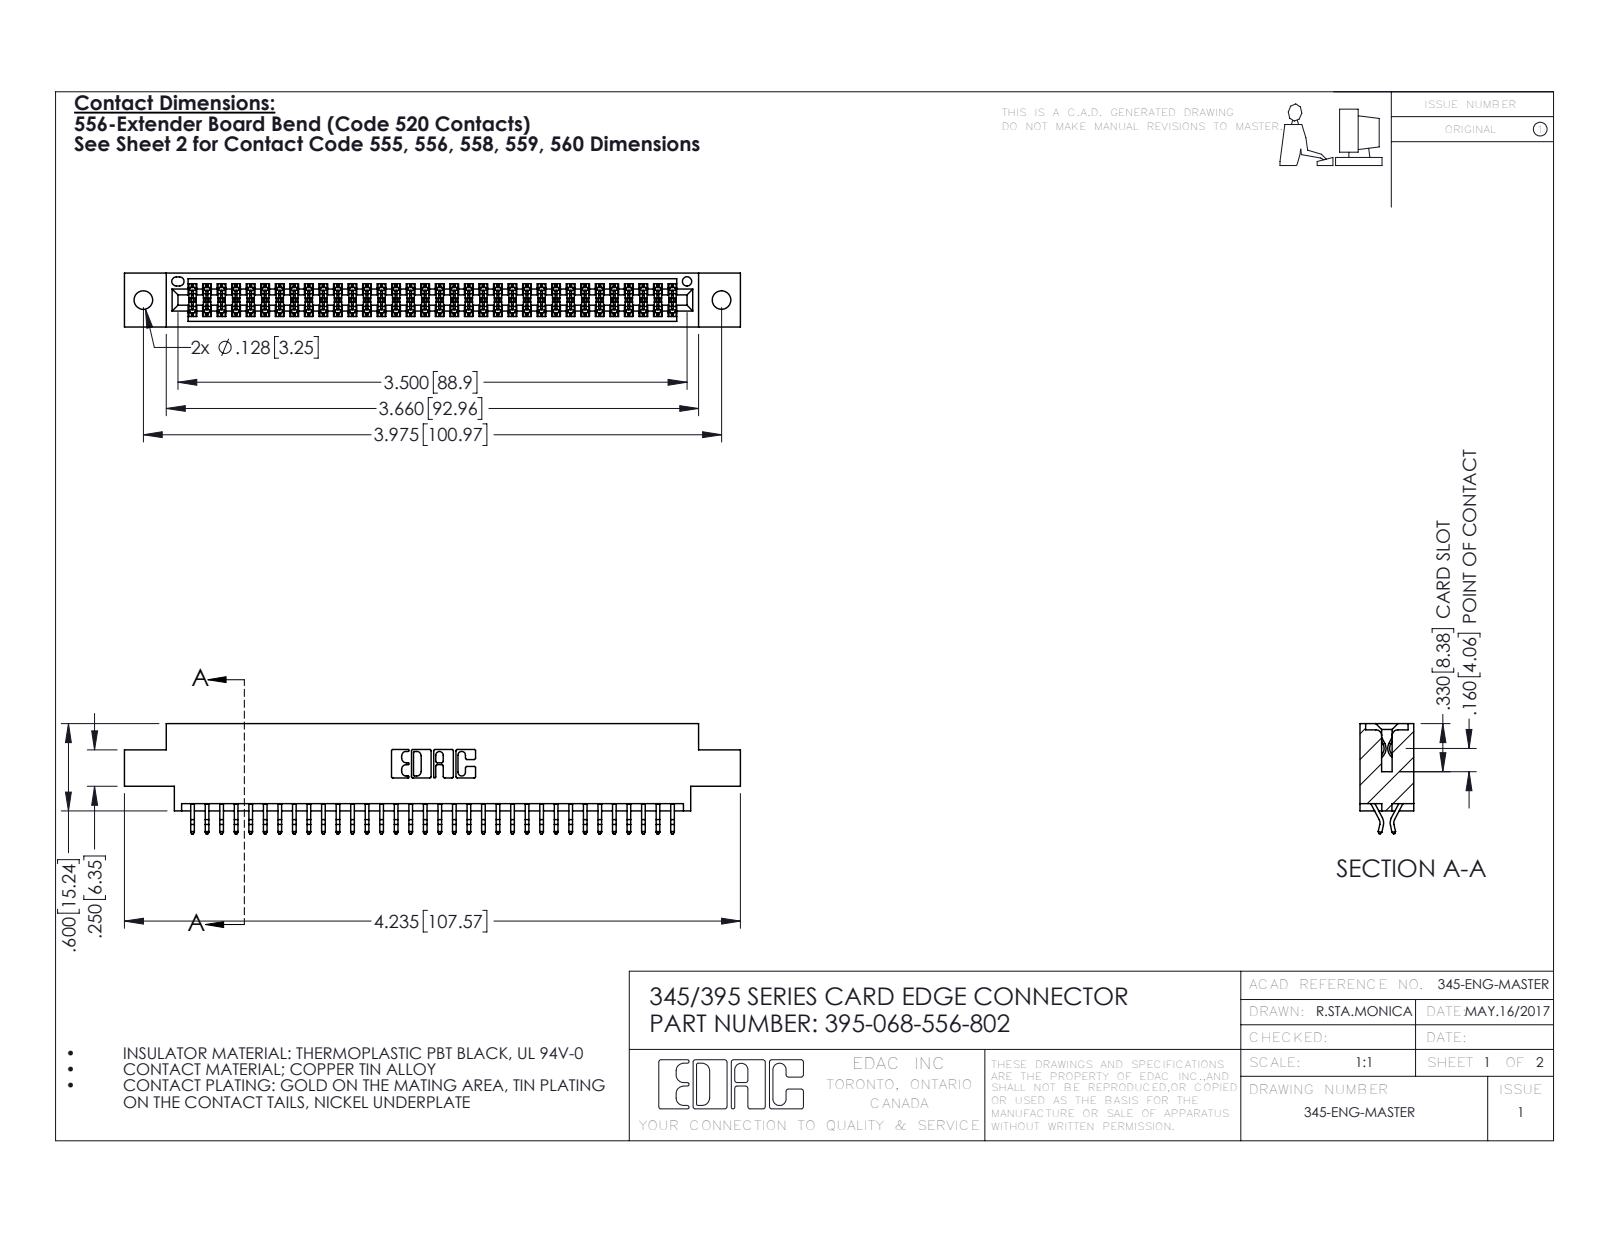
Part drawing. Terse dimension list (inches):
name: 345 Part_0.170 Offset - 0.128 Dia; 345-292-001_556 Tail; 395-068-556-802
written by: SolidWorks 2016 (CONFIG_CONTROL_DESIGN)
unit: in
bodies: 69 solids, 3938 faces (2600 planar, 1338 cylindrical, 0 other)
size: 4.235 × 0.757 × 0.37
volume: 0.624 in³; area: 22.89 in²
holes: 2× ⌀0.128, 1× ⌀0.064
rounds: 102× R0.006, 22× R0.01, 6× R0.007, 6× R0.031, 3× R0.026, 2× R0.01, 2× R0.014, 2× R0.019
face distances: 0.298, 0.072, 0.37, 0.2, 0.025, 0.098, 0.272, 0.225, 0.175, 0.149
hole spacings: 0.27, 3.74, 3.975
